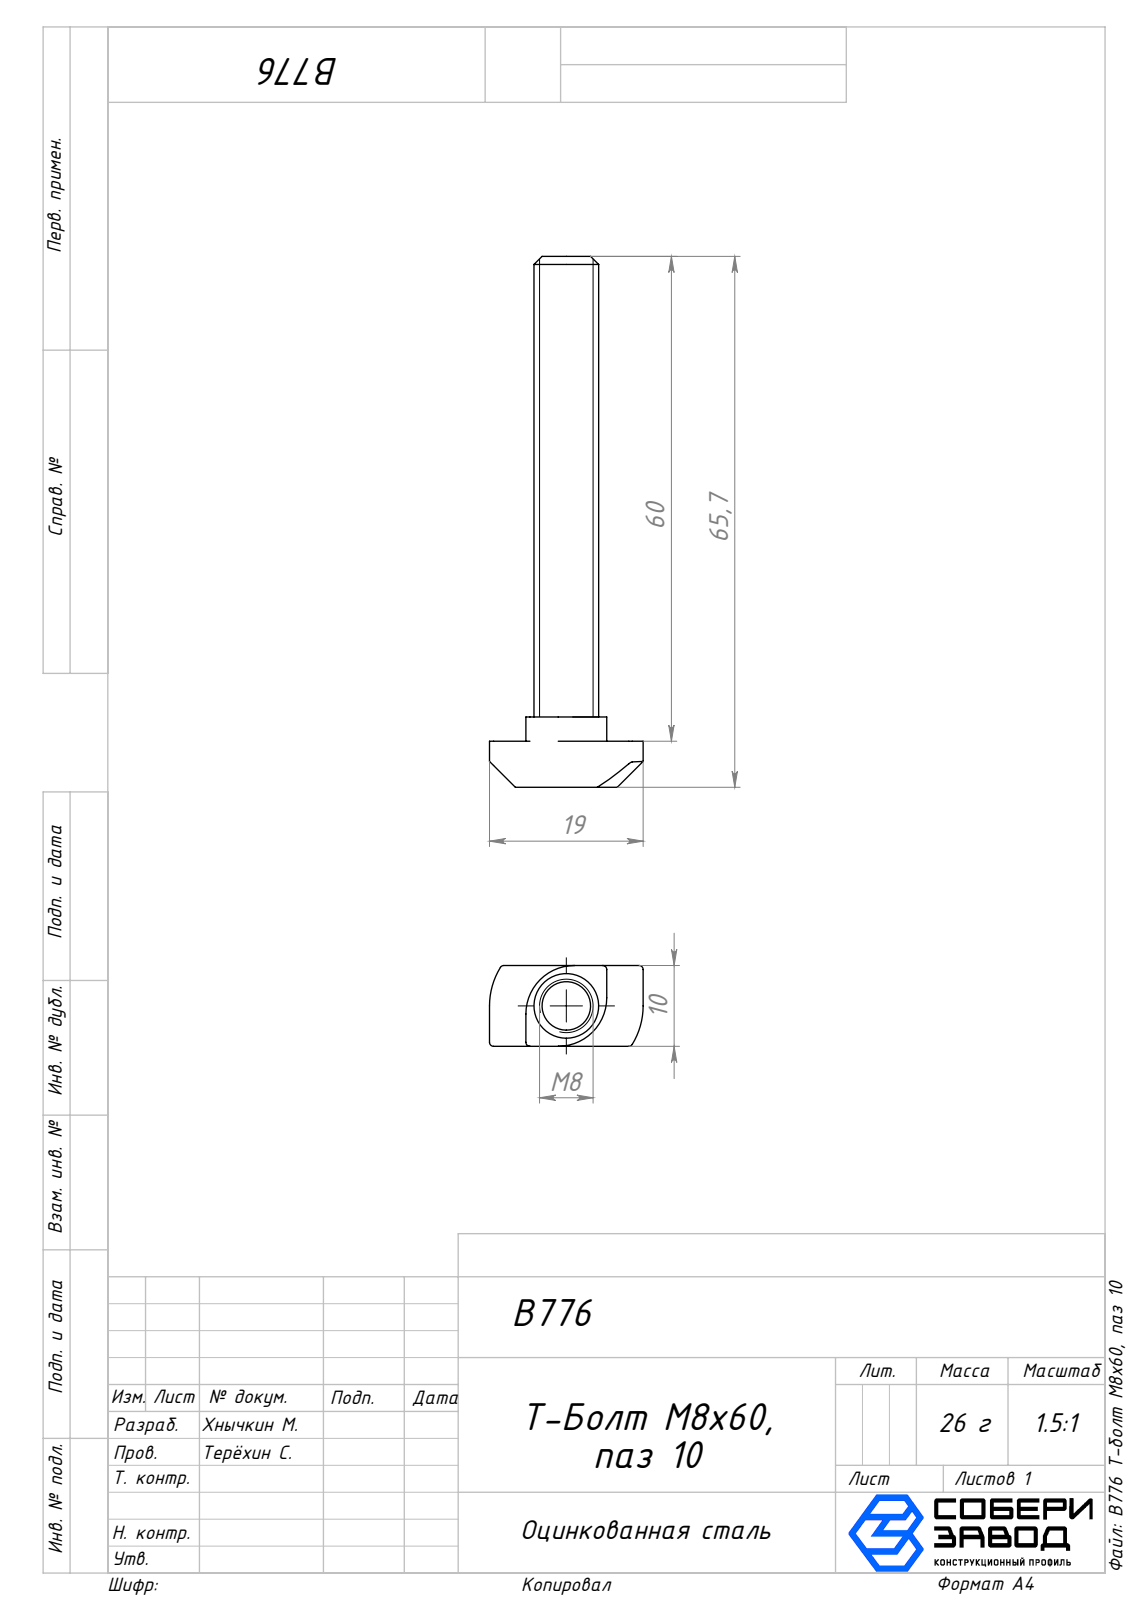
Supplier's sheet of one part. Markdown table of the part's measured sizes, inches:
| quantity | value |
| --- | --- |
| part name | B776 Т-болт М8х60, паз 10 |
| STEP written by | SolidWorks 2025 (AUTOMOTIVE_DESIGN) |
| units | inches |
| bodies | 1 solid, 29 faces (13 planar, 12 cylindrical, 4 other) |
| overall size | 2.587 × 0.748 × 0.394 |
| volume | 0.248 in³ |
| surface area | 3.325 in² |
| round bosses / shafts (diameter × count) | 0.315 × 1 |
| partial cylindrical surfaces (radius × count) | 0.02 × 6, 0.236 × 2, 0.357 × 2 |
| main face-to-face distances | 0.394, 0.224, 0.343, 0.118, 2.587, 2.362, 2.244, 0.177, 0.571, 0.748 |
